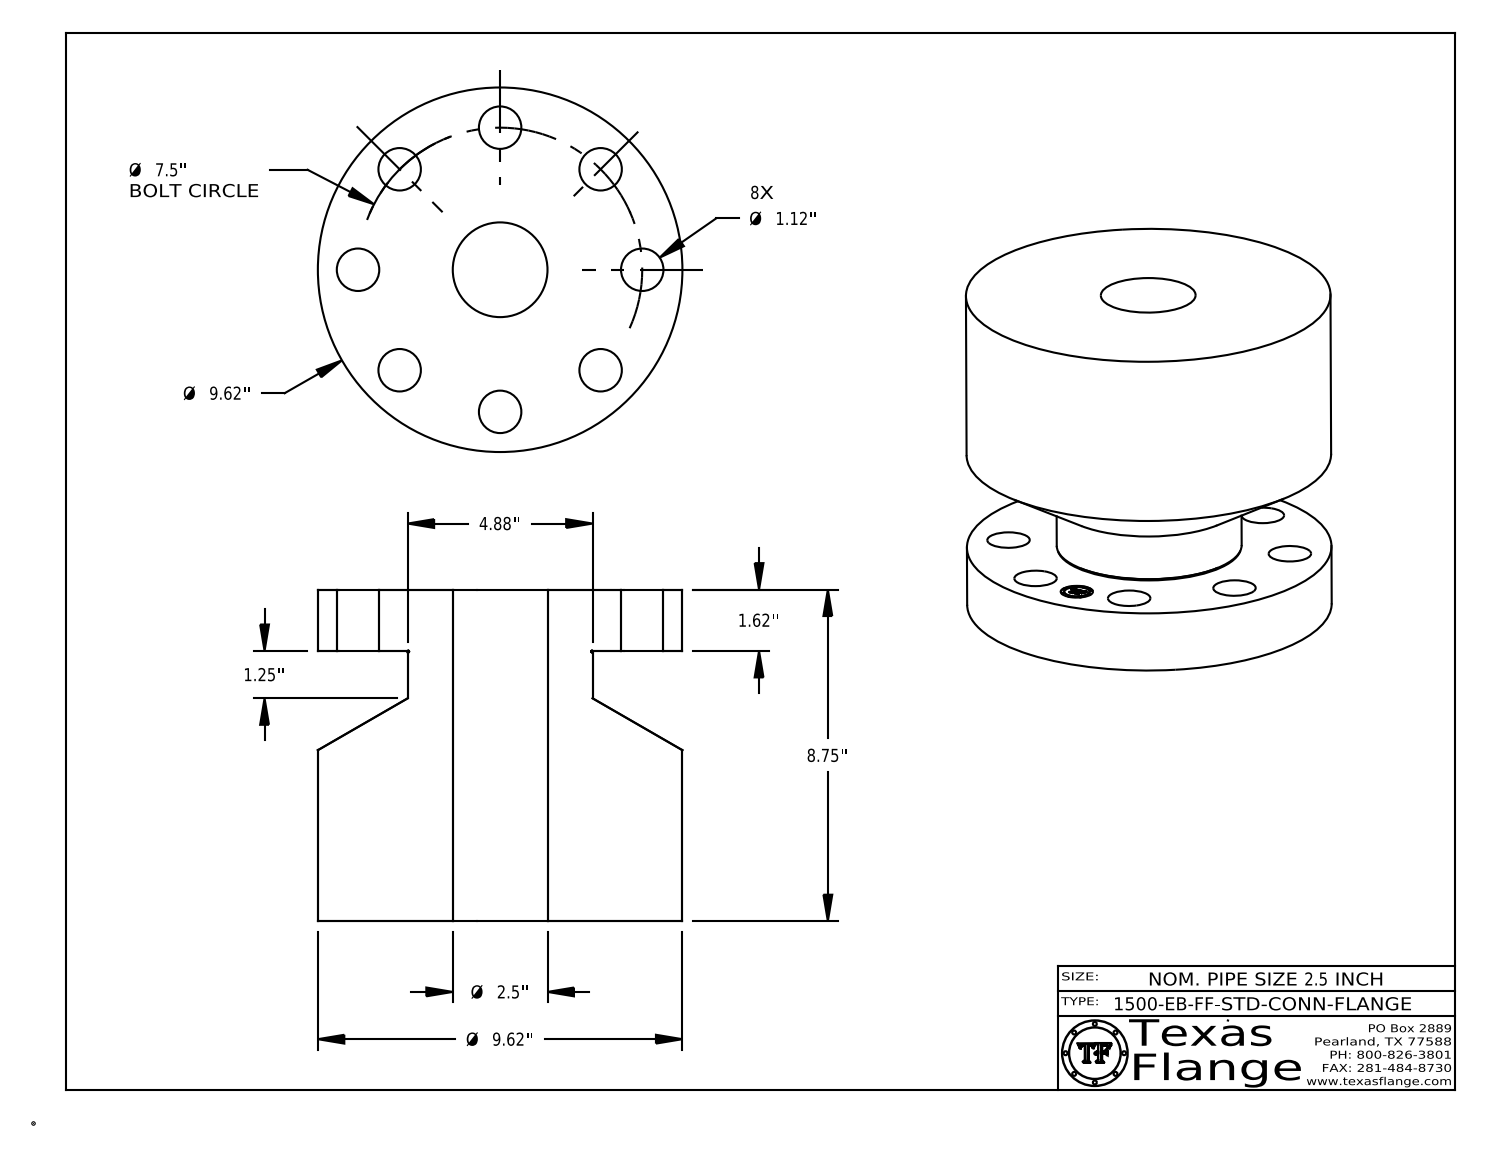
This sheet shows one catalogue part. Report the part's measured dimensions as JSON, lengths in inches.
{"part_name": "2.5-1500-EB-FF-STD-CONN-FLANGE", "step_written_by": "CATIA V5 STEP AP214 (AUTOMOTIVE_DESIGN)", "units": "inches", "bodies": {"solids": 1, "faces": 418, "planar": 368, "cylindrical": 44, "other": 6}, "overall_size": [9.62, 9.62, 8.75], "volume_in3": 471.8, "surface_area_in2": 555.5, "round_holes": [[1.12, 8], [0.85, 1], [2.5, 1]], "round_bosses_or_shafts": [[0.051, 8], [9.62, 1], [4.88, 1], [0.67, 1]], "face_to_face_distances": [8.75, 1.62, 7.13, 1.615, 7.135, 0.254, 0.248, 0.046, 0.164, 0.211], "hole_center_spacings": [3.75, 2.87, 5.303, 6.929, 1.463, 6.236, 7.356, 7.5]}
